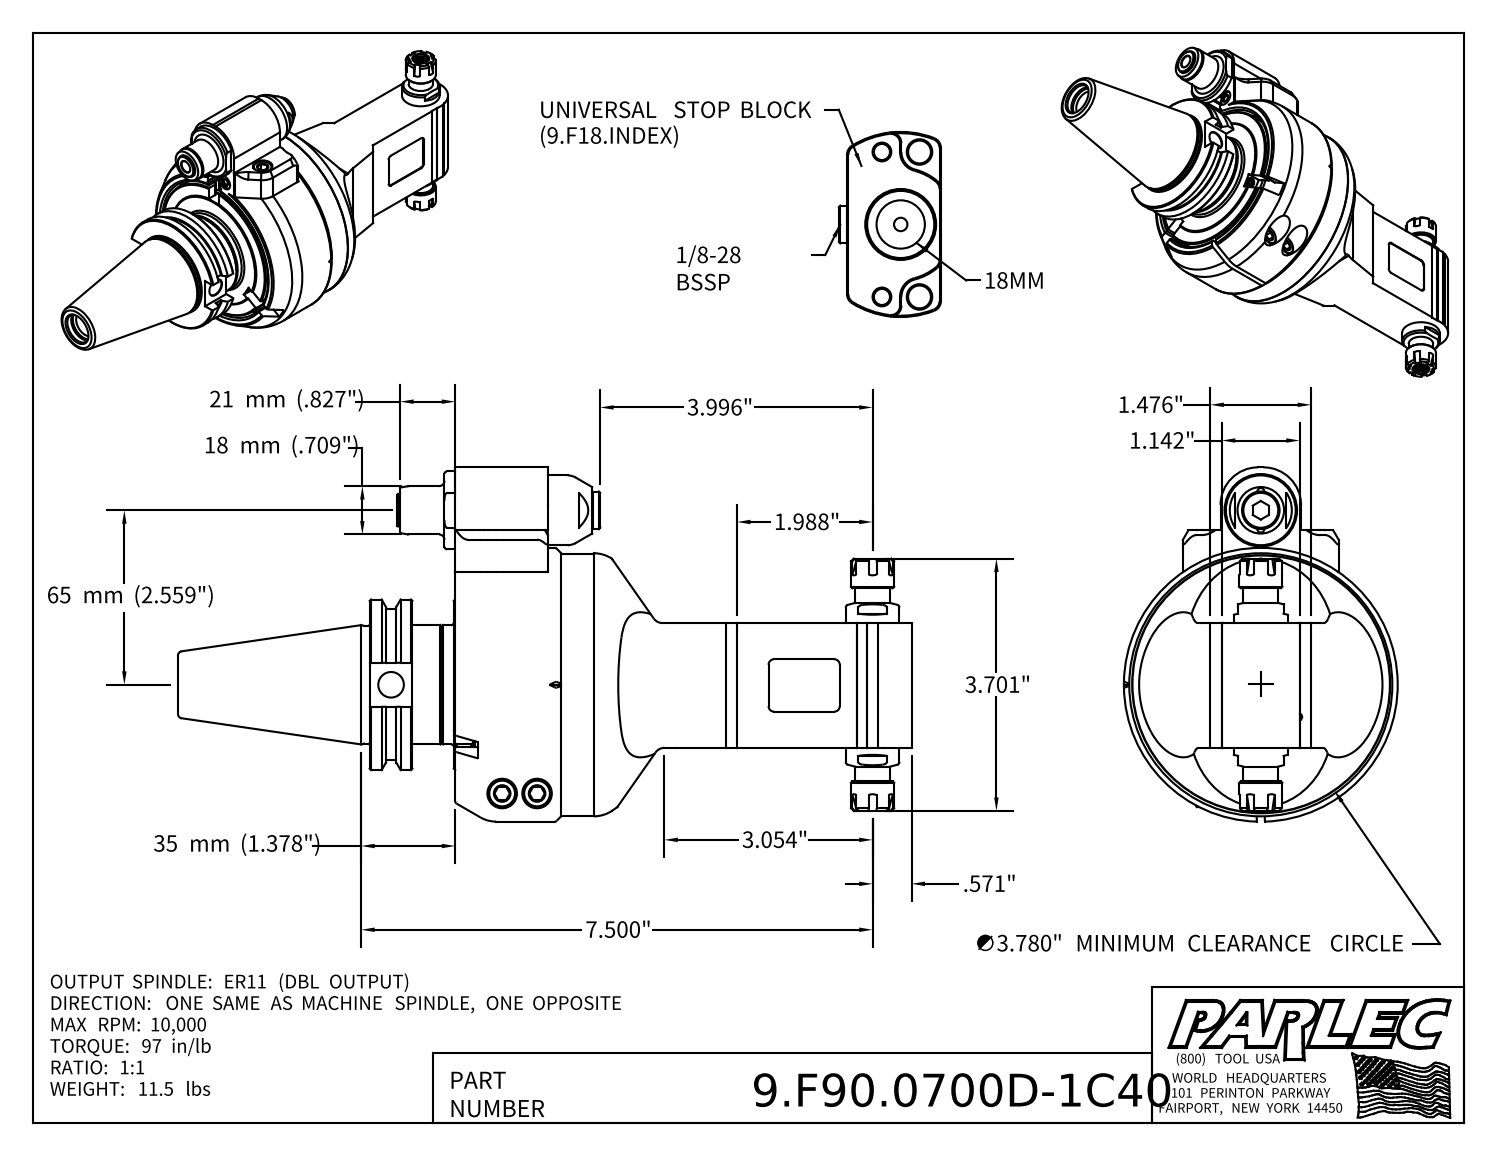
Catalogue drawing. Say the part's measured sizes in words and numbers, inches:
The part is named "9.F90.0700D-1C40; 9_GA1_446_2 (EVO, Type 1, C40, 65mm, 35mm); 9_F90_07000_2U". Its 3-D file was written by "Autodesk Inventor 2022 (AUTOMOTIVE_DESIGN)". It is 4 solids with 669 faces: 299 planar, 192 cylindrical and 178 other. Overall it measures 10.758 by 5.196 by 4.016 inches. Its volume is 48.94 cubic inches and its surface area 218.5 square inches. Round holes: 21 of diameter 0.335, 4 of diameter 0.126, 3 of diameter 0.197, 3 of diameter 0.256, 2 of diameter 0.102, 2 of diameter 0.13, 2 of diameter 0.165, 2 of diameter 0.315, 2 of diameter 0.409, 2 of diameter 0.413, 2 of diameter 0.433, 2 of diameter 0.492. Round bosses or shafts: 4 of diameter 0.394, 2 of diameter 0.709, 2 of diameter 0.472, 2 of diameter 0.315, 2 of diameter 0.236, 2 of diameter 0.098, 1 of diameter 4.016, 1 of diameter 3.85. Partial cylindrical surfaces (rounded edges, fillets, slot ends): 14 of radius 0.039, 12 of radius 0.079, 12 of radius 1.181, 6 of radius 0.118, 4 of radius 0.157, 2 of radius 0.02, 2 of radius 0.315, 2 of radius 0.551. The main face-to-face distances are 0.02, 0.276, 0.039, 0.295, 1.26, 0.335, 1.831, 1.555, 1.142, 1.28. The hole center spacings are 1.516, 2.144, 1.824, 3.002, 0.835, 2.651, 2.914, 0.422.
